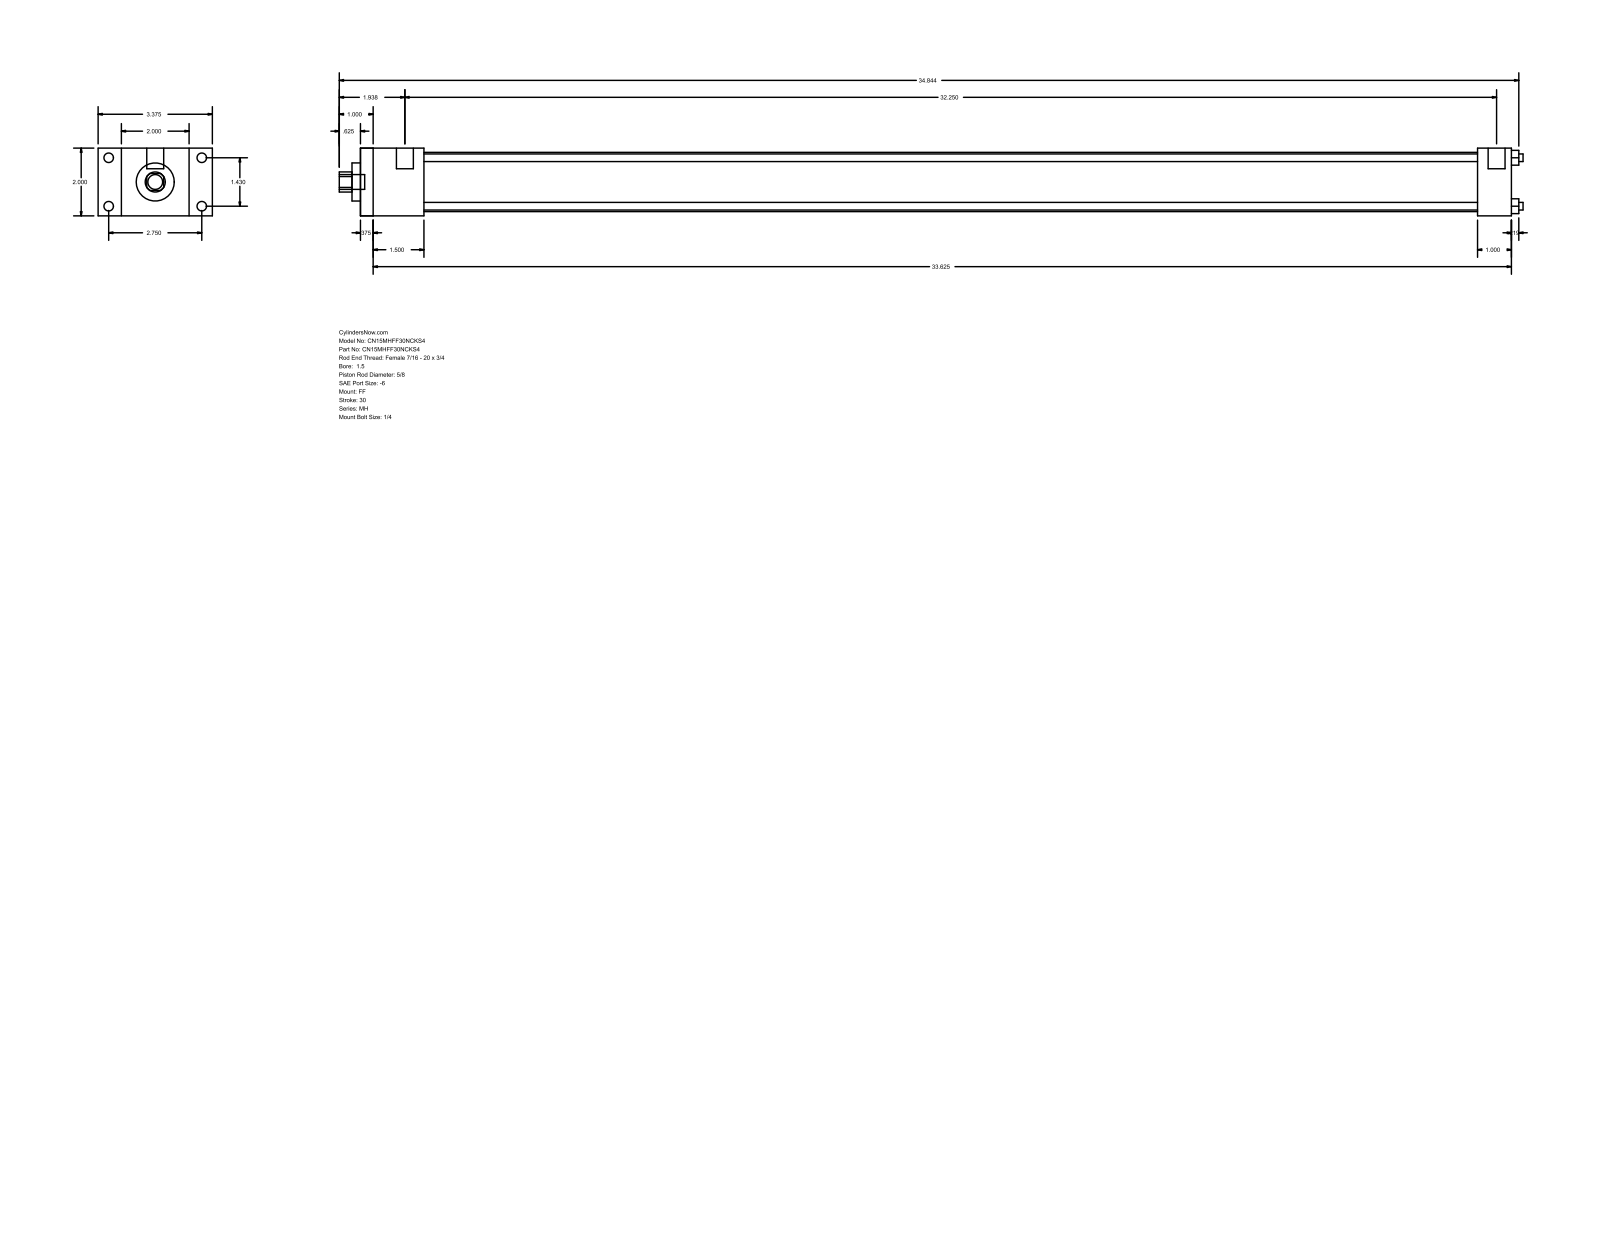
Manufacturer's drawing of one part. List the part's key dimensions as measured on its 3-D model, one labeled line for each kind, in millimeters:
Part name (STEP PRODUCT): MH_FF__0150_0.625
STEP written by: GSSL Pune (CONFIG_CONTROL_DESIGN)
Units: millimetres
Bodies: 0 solids, 92 faces (64 planar, 28 cylindrical, 0 other)
Overall size (bounding box): 888.21 × 85.72 × 50.8
Round holes (diameter × count): ⌀5.71 ×4, ⌀15.88 ×1, ⌀28.57 ×1, ⌀44.45 ×1
Round bosses / shafts (diameter × count): ⌀7.14 ×4, ⌀5.56 ×4, ⌀12.7 ×2, ⌀11.11 ×1
Partial cylindrical surfaces — rounded edges, fillets, slot ends (radius × count): R7.54 ×1
Main face-to-face distances: 50.8, 863.6, 9.52, 854.08, 25.4, 17.46, 68.26, 47.62, 38.1, 815.98
Hole centre spacings: 25.68, 36.32, 51.36
